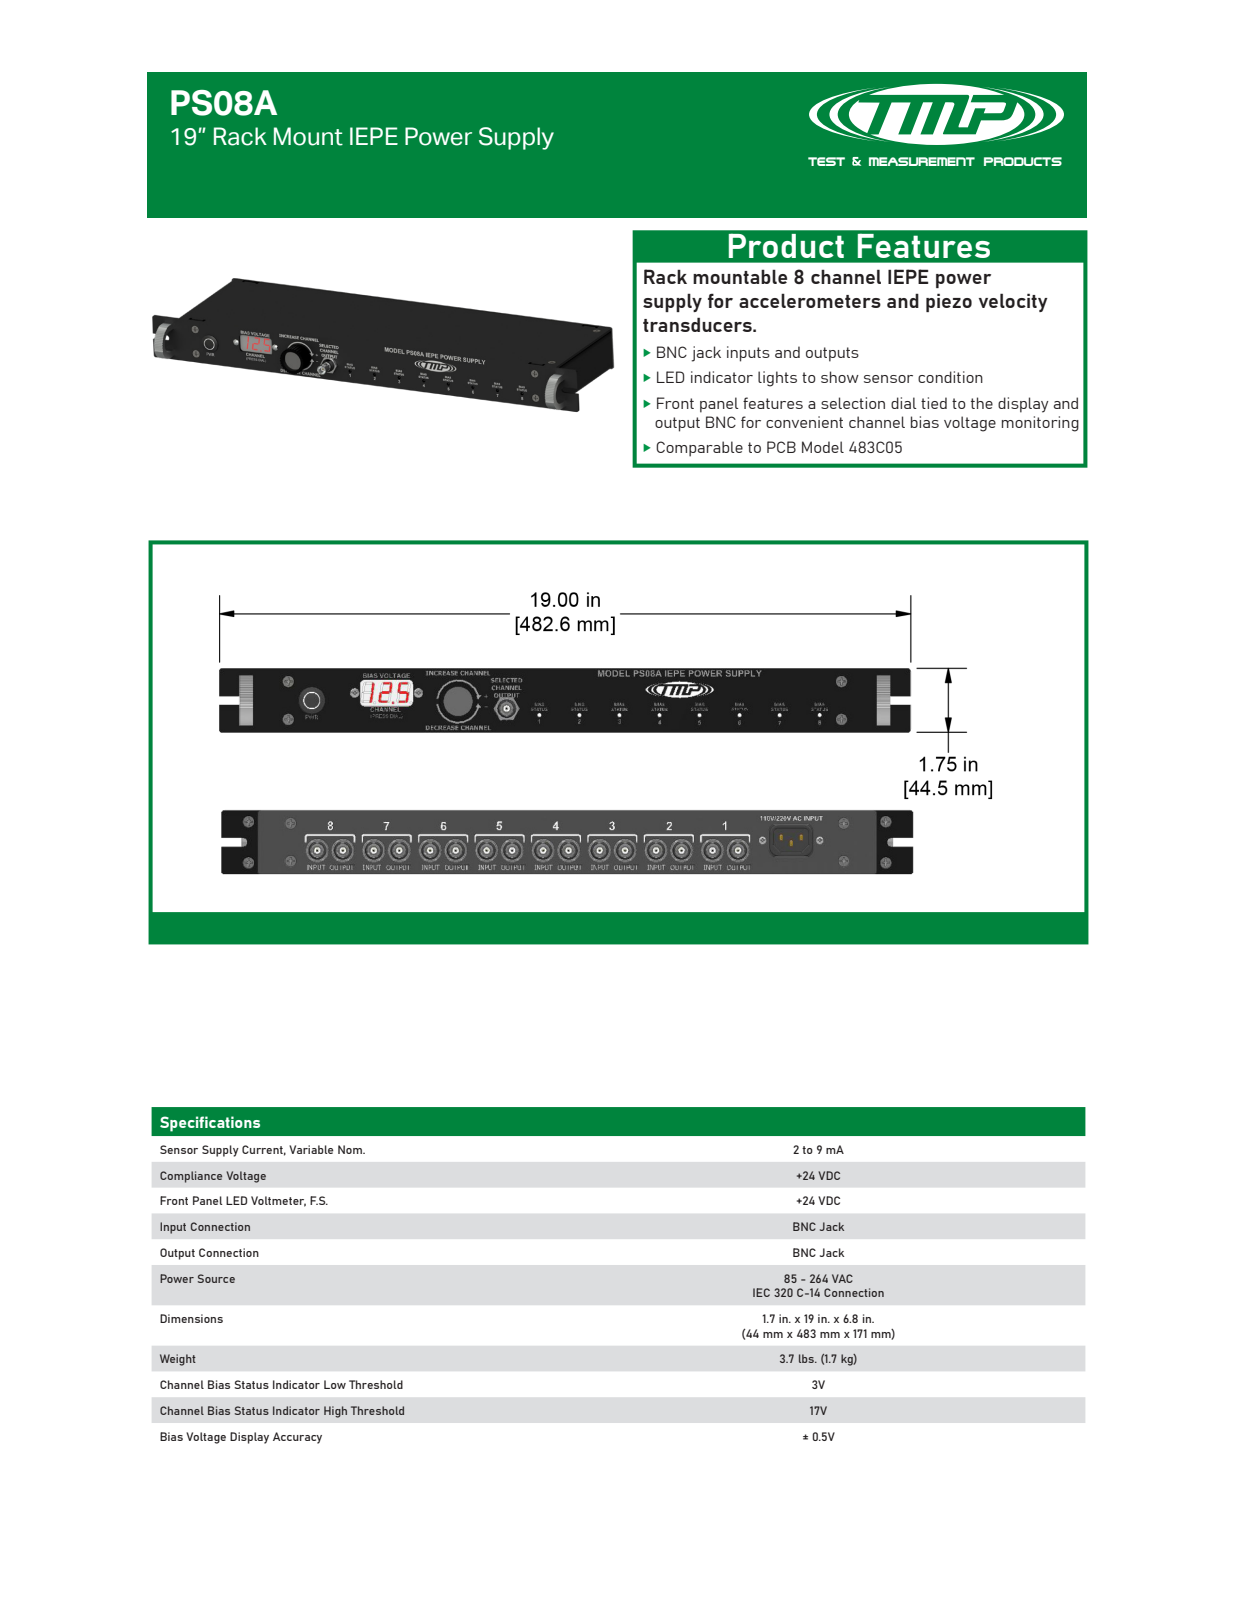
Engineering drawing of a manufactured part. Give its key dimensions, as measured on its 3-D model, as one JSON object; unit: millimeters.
{"part_name": "PS08A; JBP10923 - for PS08A; JBP10965; JBP10965, GLASS (+8 more)", "step_written_by": "Autodesk Inventor 2025 (AUTOMOTIVE_DESIGN)", "units": "millimeters", "bodies": {"solids": 134, "faces": 28528, "planar": 16851, "cylindrical": 6433, "other": 5244}, "overall_size": [482.6, 177.5, 44.5], "volume_mm3": 611100, "surface_area_mm2": 536600, "round_holes": [[2, 37], [1, 36], [0.9, 34], [6.4, 30], [1, 29], [0.9, 28], [2.1, 17], [6.8, 17], [8.1, 17], [9.3, 17], [13, 17], [11.7, 16]], "round_bosses_or_shafts": [[1.8, 34], [0.7, 34], [0.7, 34], [15.9, 17], [12.6, 17], [9.7, 17], [8.9, 17], [4.7, 17]], "partial_cylinders_radius": [[0.1, 490], [0.3, 246], [0.1, 108], [0.2, 91], [0.1, 72], [0.6, 71], [0.2, 51], [0.4, 44]], "face_to_face_distances": [2.5, 41.4, 38.9, 43.9, 7.9, 5.4, 33.5, 36, 9.3, 6.8], "hole_center_spacings": [27.9, 55.9, 83.8, 111.8, 39.4, 139.7, 5.6, 29.2]}
